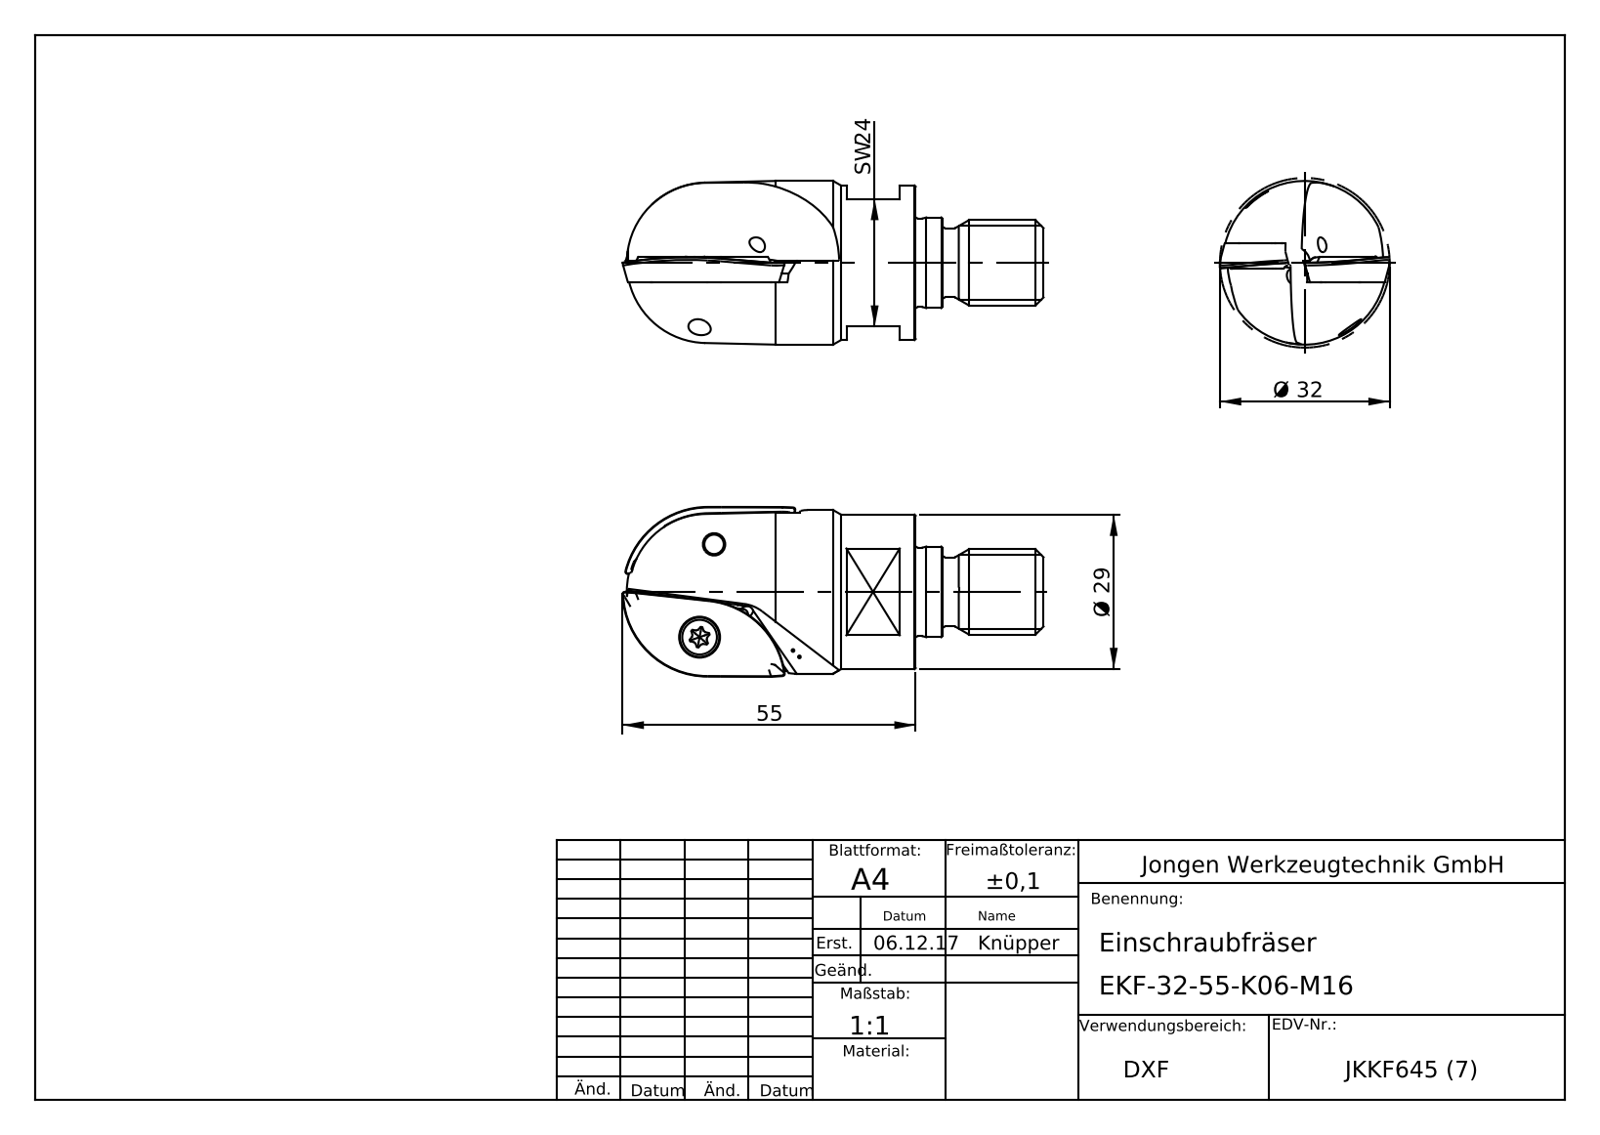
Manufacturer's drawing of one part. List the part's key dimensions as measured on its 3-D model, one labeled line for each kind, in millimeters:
Part name (STEP PRODUCT): EKF-32-55-K06-M16
STEP written by: SolidWorks 2019 (AUTOMOTIVE_DESIGN)
Units: millimetres
Bodies: 1 solid, 132 faces (33 planar, 27 cylindrical, 72 other)
Overall size (bounding box): 79 × 31.9 × 31.9
Volume: 39 720 mm³ · Surface area: 8 631 mm²
Round holes (diameter × count): ⌀2.5 ×2, ⌀4 ×1
Round bosses / shafts (diameter × count): ⌀30.72 ×1, ⌀29 ×1, ⌀17 ×1, ⌀16.6 ×1, ⌀16 ×1, ⌀13 ×1
Partial cylindrical surfaces — rounded edges, fillets, slot ends (radius × count): R0.2 ×4, R5 ×1, R7 ×1
Main face-to-face distances: 24, 11.57, 12.43, 5, 19, 10, 13, 18, 37, 3
